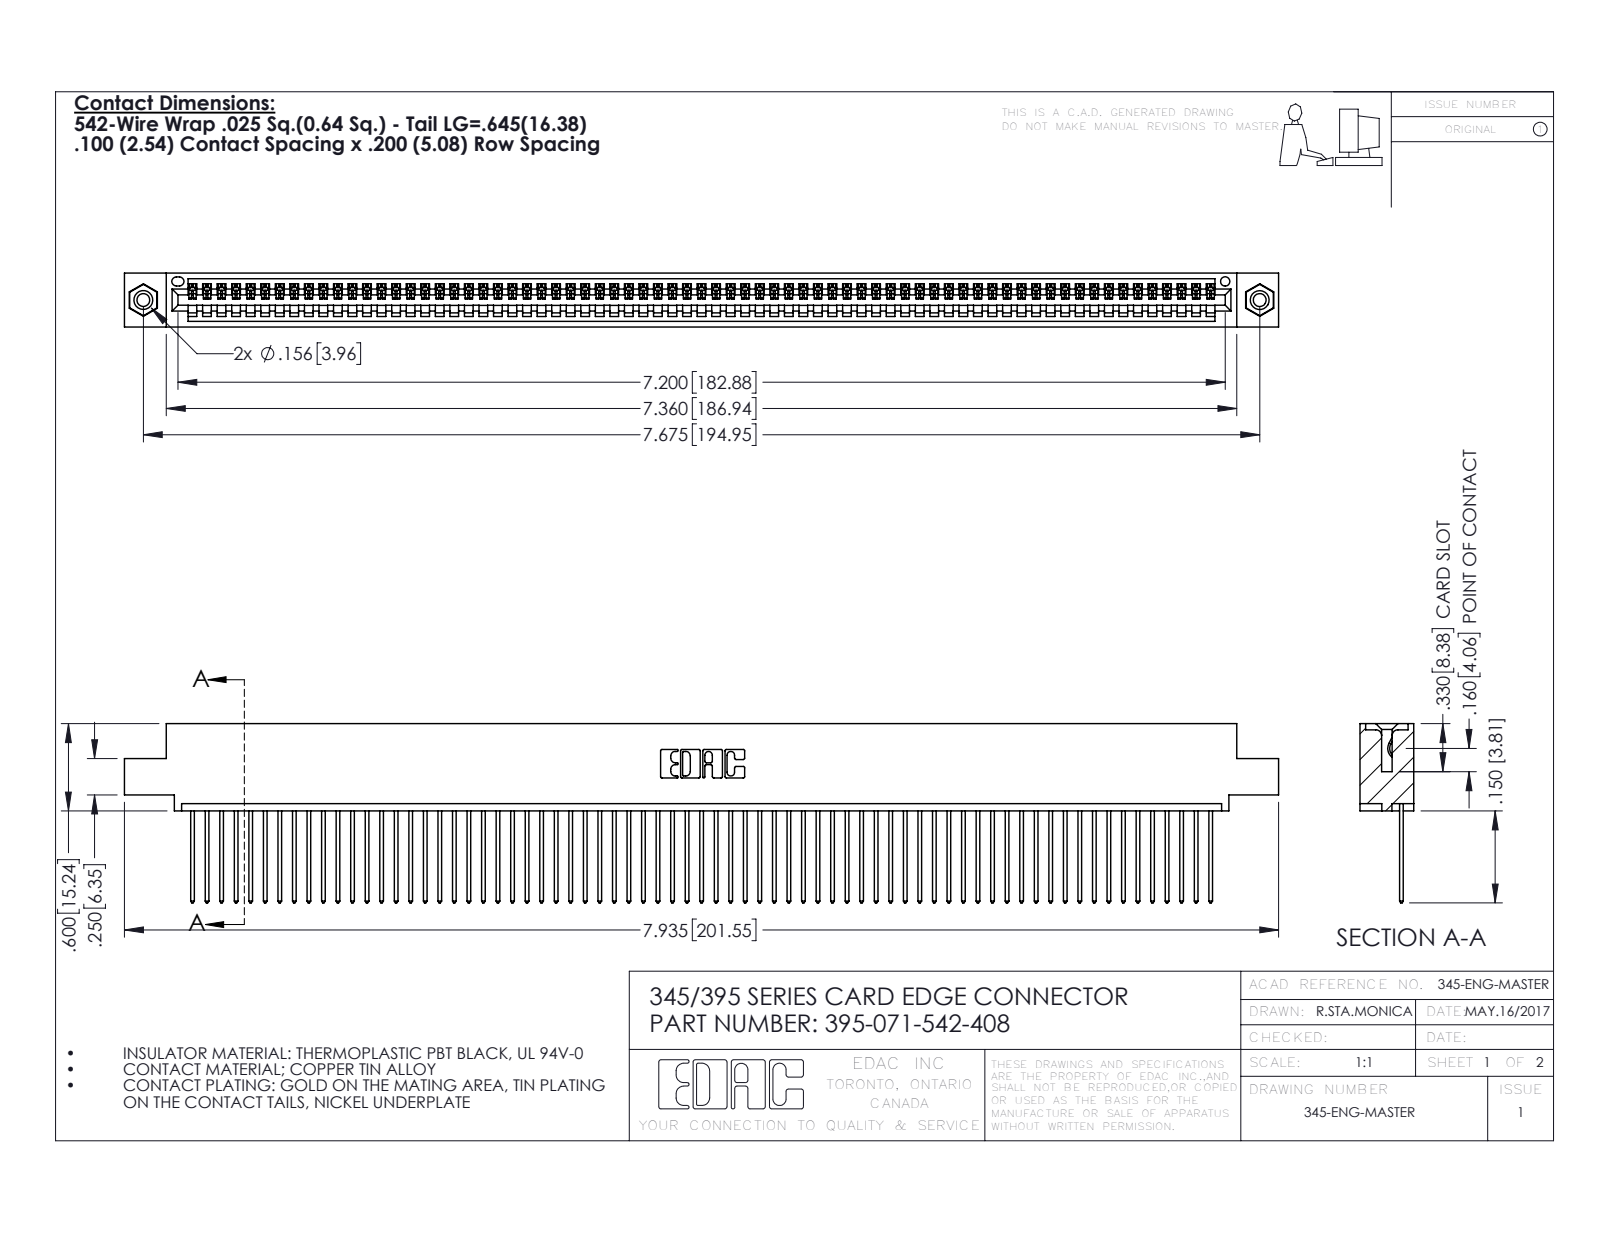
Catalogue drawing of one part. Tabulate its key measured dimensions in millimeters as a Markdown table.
| quantity | value |
| --- | --- |
| part name | 345-292-001_345-293-142; 345-250-001_345-250-003-102; 345 Part_0.110 Offset - 0.156 Dia-TI; 395-071-542-408 |
| STEP written by | SolidWorks 2016 (CONFIG_CONTROL_DESIGN) |
| units | millimeters |
| bodies | 74 solids, 4308 faces (2956 planar, 1336 cylindrical, 16 other) |
| overall size | 201.5 × 31.3 × 9.4 |
| volume | 19 450 mm³ |
| surface area | 27 350 mm² |
| round holes (diameter × count) | 2.3 × 2, 3.2 × 2, 4 × 2, 1.6 × 1 |
| round bosses / shafts (diameter × count) | 3.9 × 2 |
| partial cylindrical surfaces (radius × count) | 0.2 × 142, 0.3 × 142, 0.3 × 22, 0.2 × 6, 0.8 × 6, 0.7 × 3, 0.8 × 2, 1 × 2 |
| main face-to-face distances | 1.8, 7.6, 2.5, 6.9, 0.6, 9.4, 5.1, 5.7, 3.8, 1.8 |
| hole center spacings | 6.9, 189, 194.9 |
